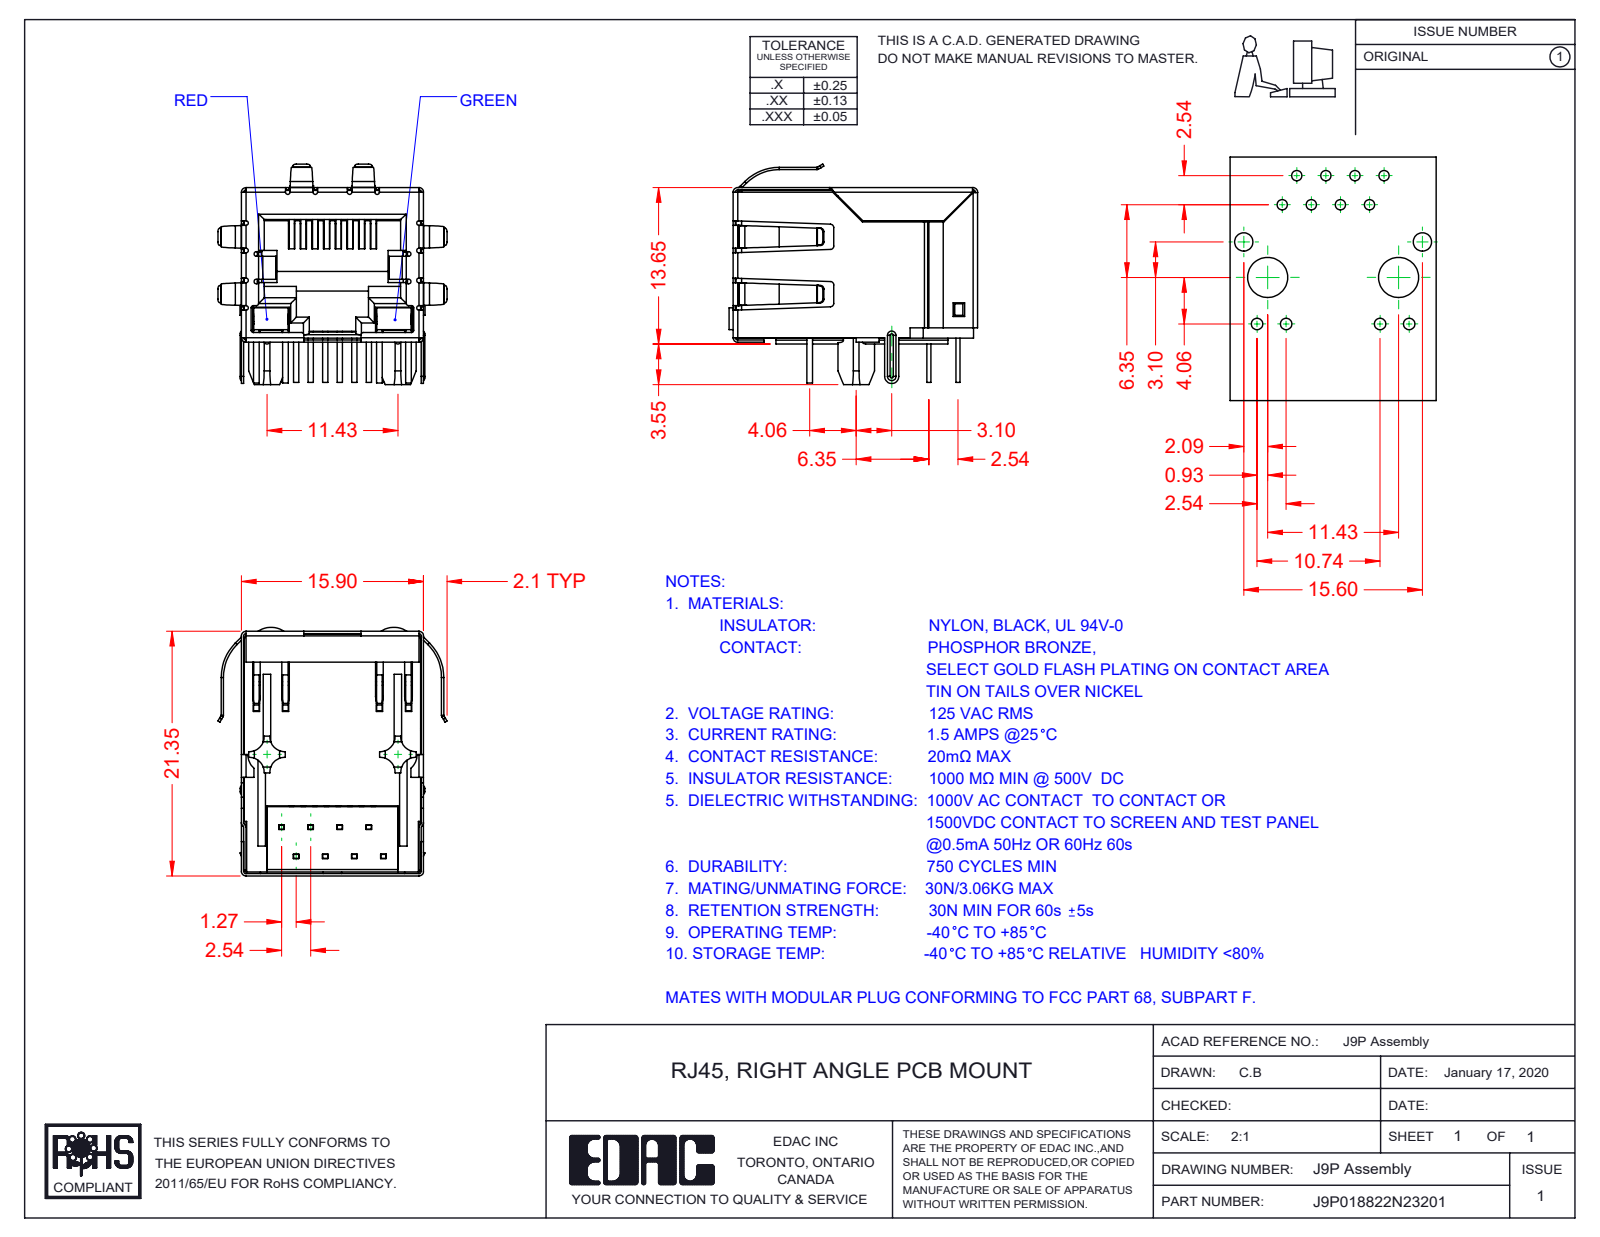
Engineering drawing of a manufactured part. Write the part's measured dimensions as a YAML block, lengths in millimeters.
part_name: "9P-LED Insulator; 9P-LED LED LH_2-Red; 9P-LED LED RH_3-Green; 9P-LED Contacts (+4 more)"
step_written_by: "SolidWorks 2016 (CONFIG_CONTROL_DESIGN)"
units: millimeters
bodies: {solids: 13, faces: 1472, planar: 1042, cylindrical: 336, other: 94}
overall_size: [21.7, 20, 19.25]
volume: 2687
surface_area: 7515
partial_cylinders:
  - {radius: 0.2, count: 39}
  - {radius: 0.5, count: 22}
  - {radius: 0.3, count: 20}
  - {radius: 0.4, count: 16}
  - {radius: 1.3, count: 8}
  - {radius: 0.23, count: 5}
  - {radius: 0.11, count: 4}
  - {radius: 0.31, count: 4}
face_to_face_distances: [15.45, 15.7, 15.65, 0.35, 0.54, 15.5, 12.36, 0.6, 1.4, 0.59]
